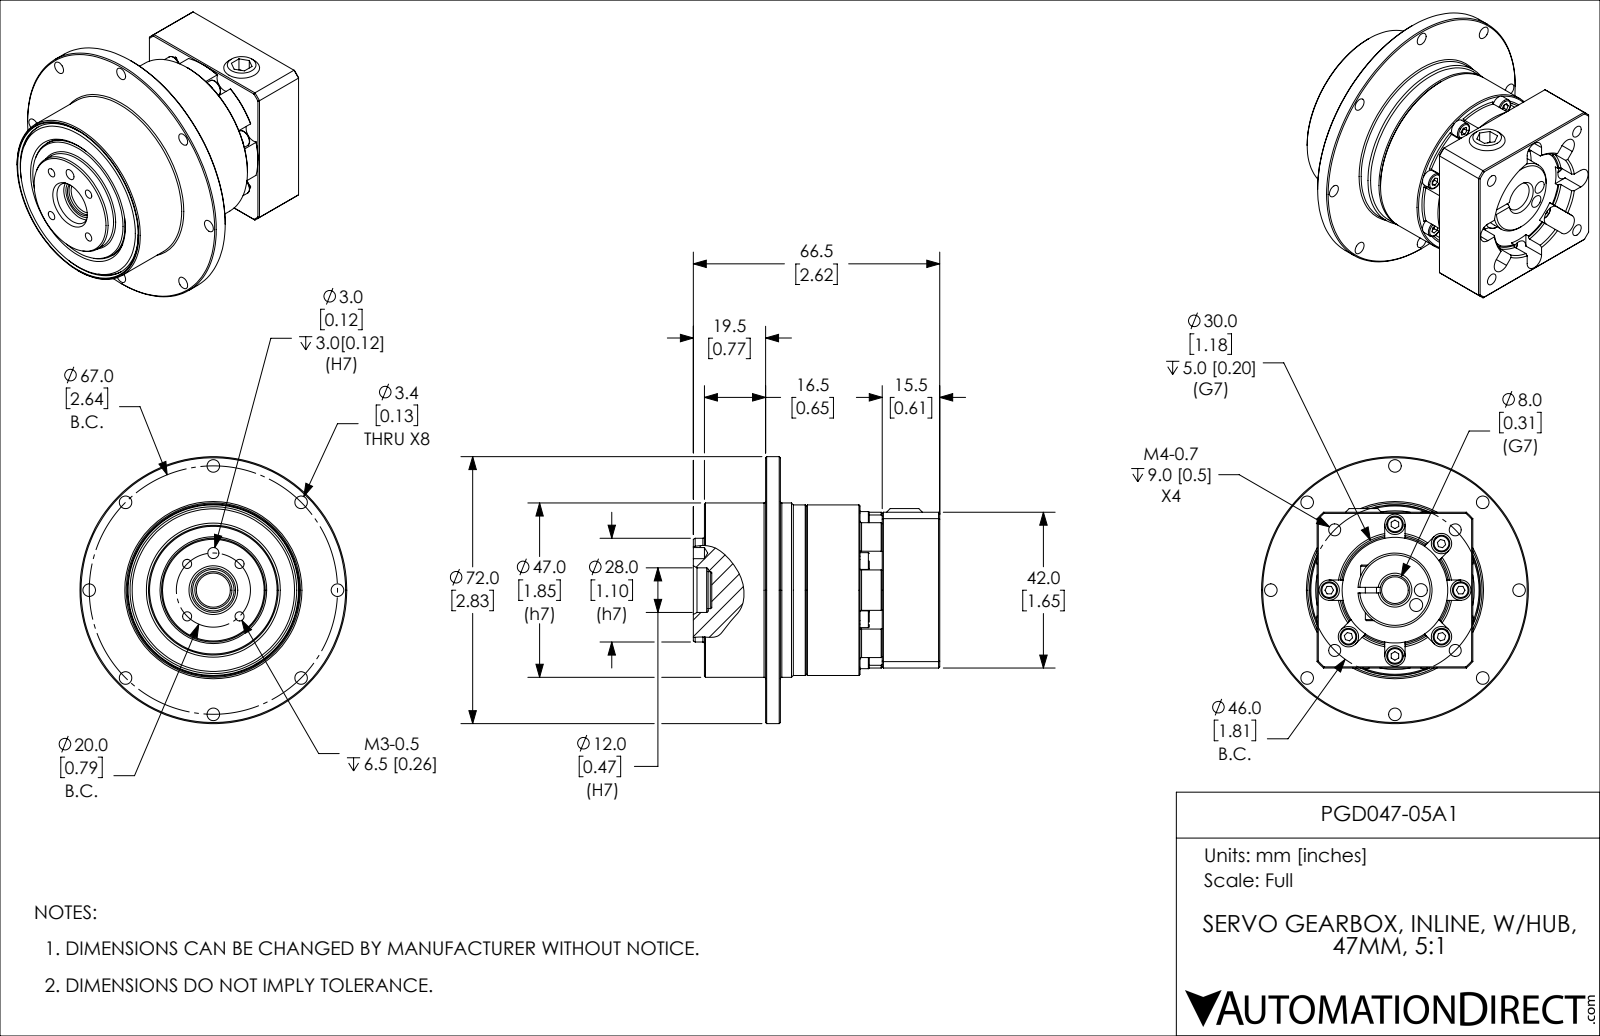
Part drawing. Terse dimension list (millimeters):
name: PGD047-05A1
written by: SolidWorks 2015 (AUTOMOTIVE_DESIGN)
unit: mm
bodies: 6 solids, 498 faces (278 planar, 147 cylindrical, 73 other)
size: 72 × 72 × 66.5
volume: 106 660 mm³; area: 32 258 mm²
holes: 8× ⌀3.4, 8× ⌀5.5, 4× ⌀2.46, 4× ⌀3.24, 2× ⌀3.5, 1× ⌀3, 1× ⌀4.9, 1× ⌀6.69, 1× ⌀8, 1× ⌀9.2, 1× ⌀11.2, 1× ⌀28.5
bosses: 9× ⌀4.5, 7× ⌀4, 1× ⌀72, 1× ⌀47, 1× ⌀46, 1× ⌀28, 1× ⌀20, 1× ⌀19
rounds: 8× R2.75, 1× R3.25, 1× R21, 1× R28.5
face distances: 3.5, 11, 4, 7, 7.5, 24, 20.5, 27.5, 42, 16.5
hole spacings: 24.42, 37.91, 47.73, 25.81, 27.36, 34.96, 12.81, 15.75
